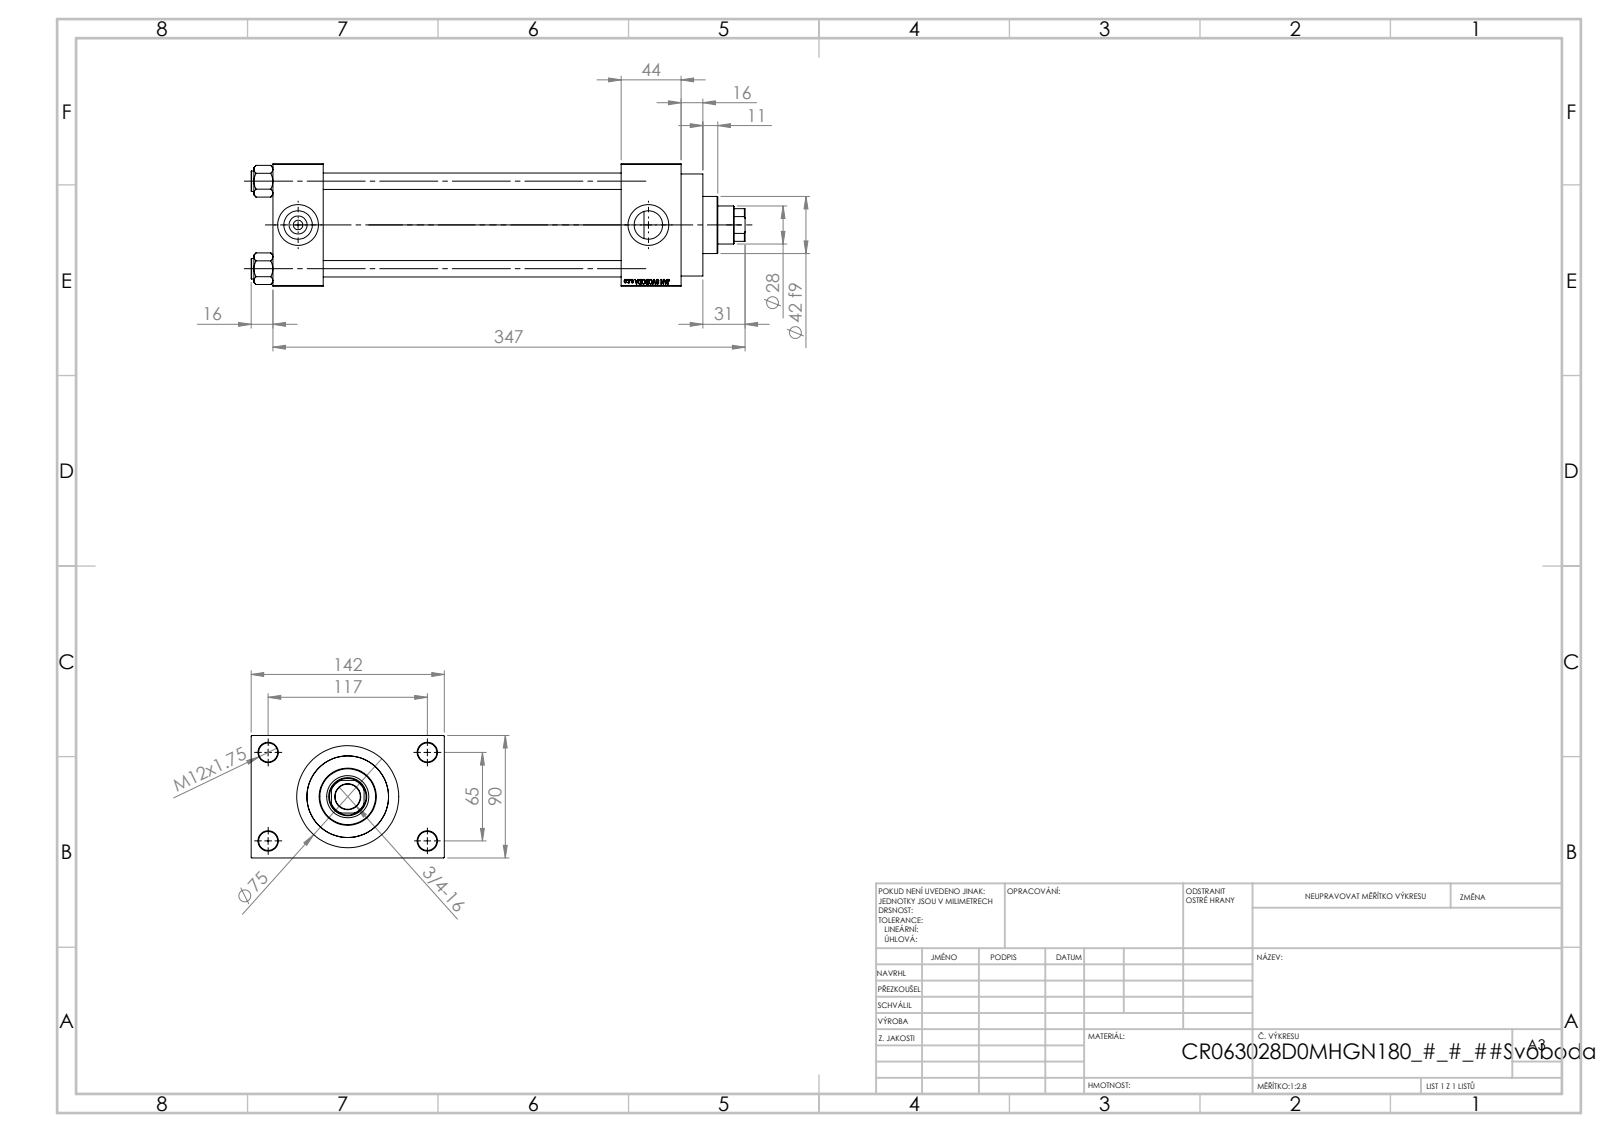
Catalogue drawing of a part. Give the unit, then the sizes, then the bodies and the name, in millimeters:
Units: millimetres
Overall size (bounding box): 363 × 142 × 90
Round holes (diameter × count): ⌀12 ×4, ⌀14 ×4, ⌀7 ×2, ⌀20.96 ×2, ⌀30 ×2, ⌀18.5 ×1, ⌀28 ×1, ⌀31 ×1, ⌀50 ×1, ⌀60 ×1, ⌀63 ×1
Round bosses / shafts (diameter × count): ⌀15 ×4, ⌀75 ×1, ⌀69 ×1, ⌀42 ×1
Partial cylindrical surfaces — rounded edges, fillets, slot ends (radius × count): R13.5 ×1
Main face-to-face distances: 90, 219, 37, 256, 263, 300, 44, 26, 116, 16
Hole centre spacings: 26.35, 45.47, 64.3, 66.92, 69.81, 90.65, 111.34, 65
Volume: 1 367 000 mm³ · Surface area: 304 866 mm²
Bodies: 11 solids, 1103 faces (497 planar, 88 cylindrical, 518 other)
Part name (STEP PRODUCT): V215CR_VCP_D; V215CR_D_TYCINKA; V215_VC_A; NUT_M5_D (+1 more)
STEP written by: SolidWorks 2019 (CONFIG_CONTROL_DESIGN)
